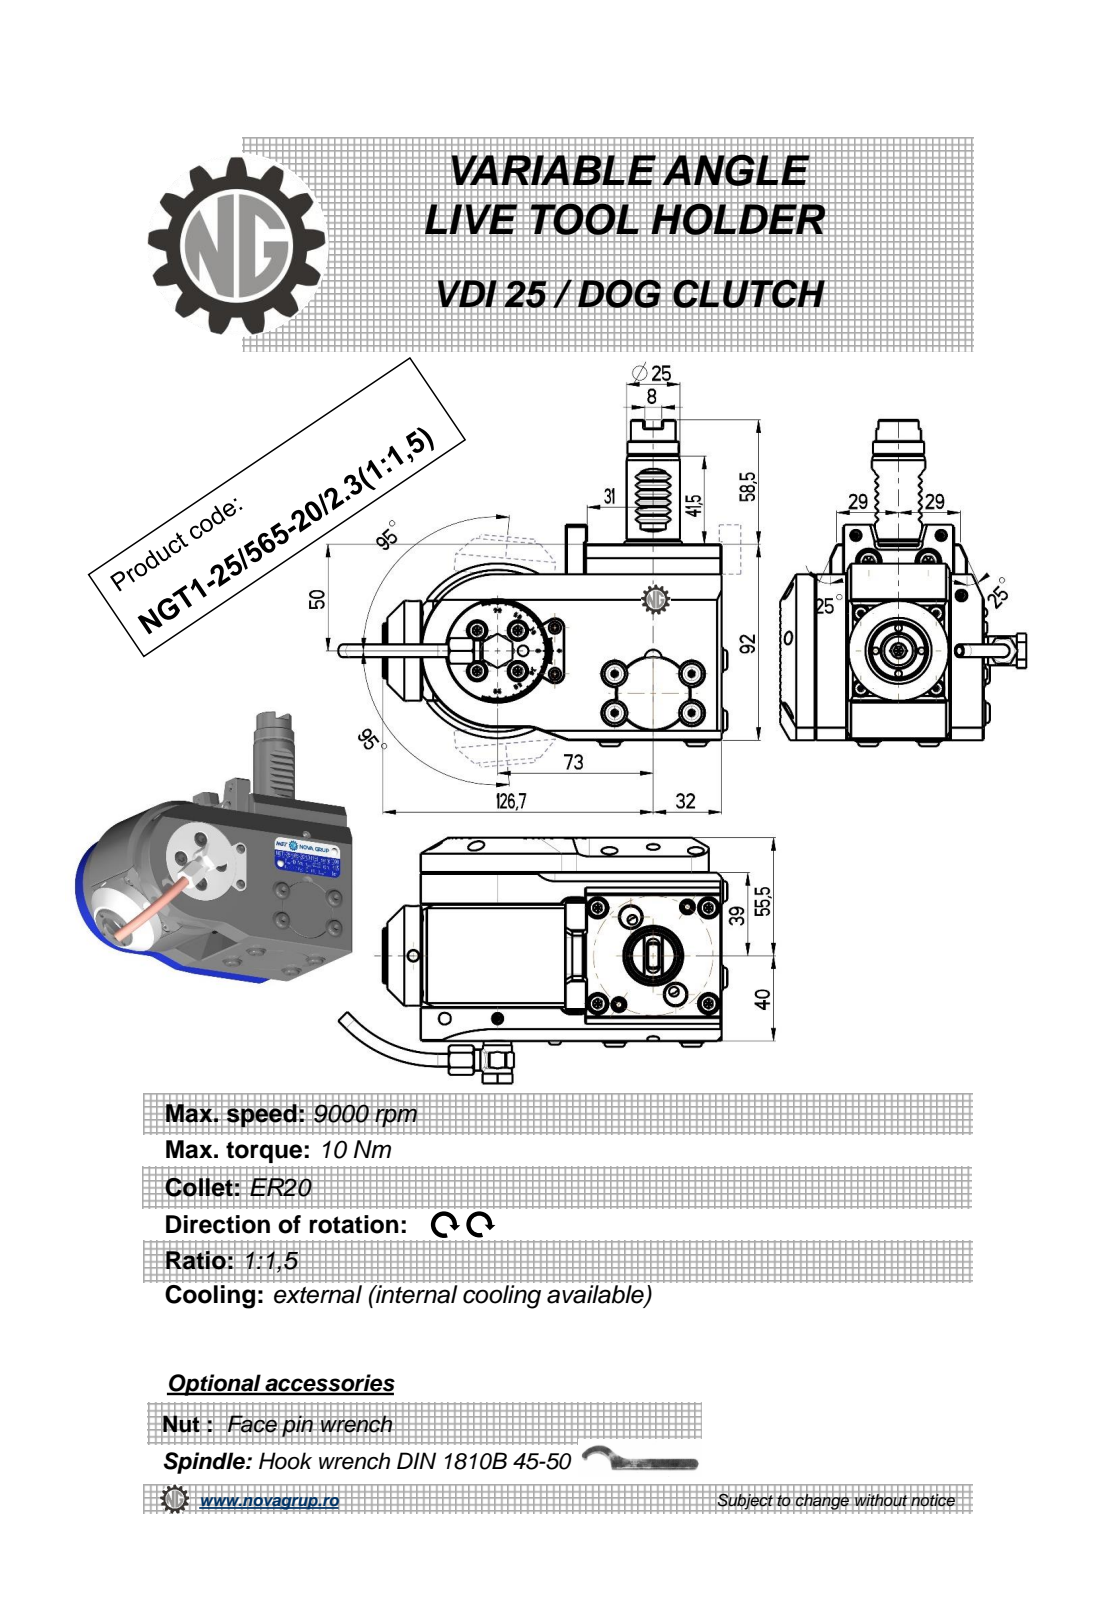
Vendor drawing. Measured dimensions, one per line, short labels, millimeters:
name: NGT1_25_565_20_1_3_1_1_5
written by: PRO/ENGINEER BY PARAMETRIC TECHNOLOGY CORPORATION, 2010280 (CONFIG_CONTROL_DESIGN)
unit: mm
bodies: 1 solid, 1185 faces (591 planar, 341 cylindrical, 253 other)
size: 182.42 × 153.25 × 115.4
volume: 1 014 000 mm³; area: 88 339 mm²
holes: 6× ⌀7.5, 5× ⌀4, 4× ⌀3.2, 3× ⌀6, 2× ⌀3.24, 2× ⌀4.2, 2× ⌀5, 1× ⌀3, 1× ⌀6.2, 1× ⌀9, 1× ⌀11, 1× ⌀16
bosses: 12× ⌀11.8, 12× ⌀9.5, 6× ⌀7, 2× ⌀10, 2× ⌀5.7, 1× ⌀82, 1× ⌀47, 1× ⌀34
rounds: 60× R0.24, 34× R0.14, 12× R0.3, 10× R0.26, 7× R8, 6× R0.2, 6× R0.5, 2× R1
face distances: 92, 16.5, 95.5, 16, 64, 56.5, 14, 8, 48, 6
hole spacings: 10.75, 15.2, 21.5, 29.73, 40.5, 40.64, 46, 47.83
